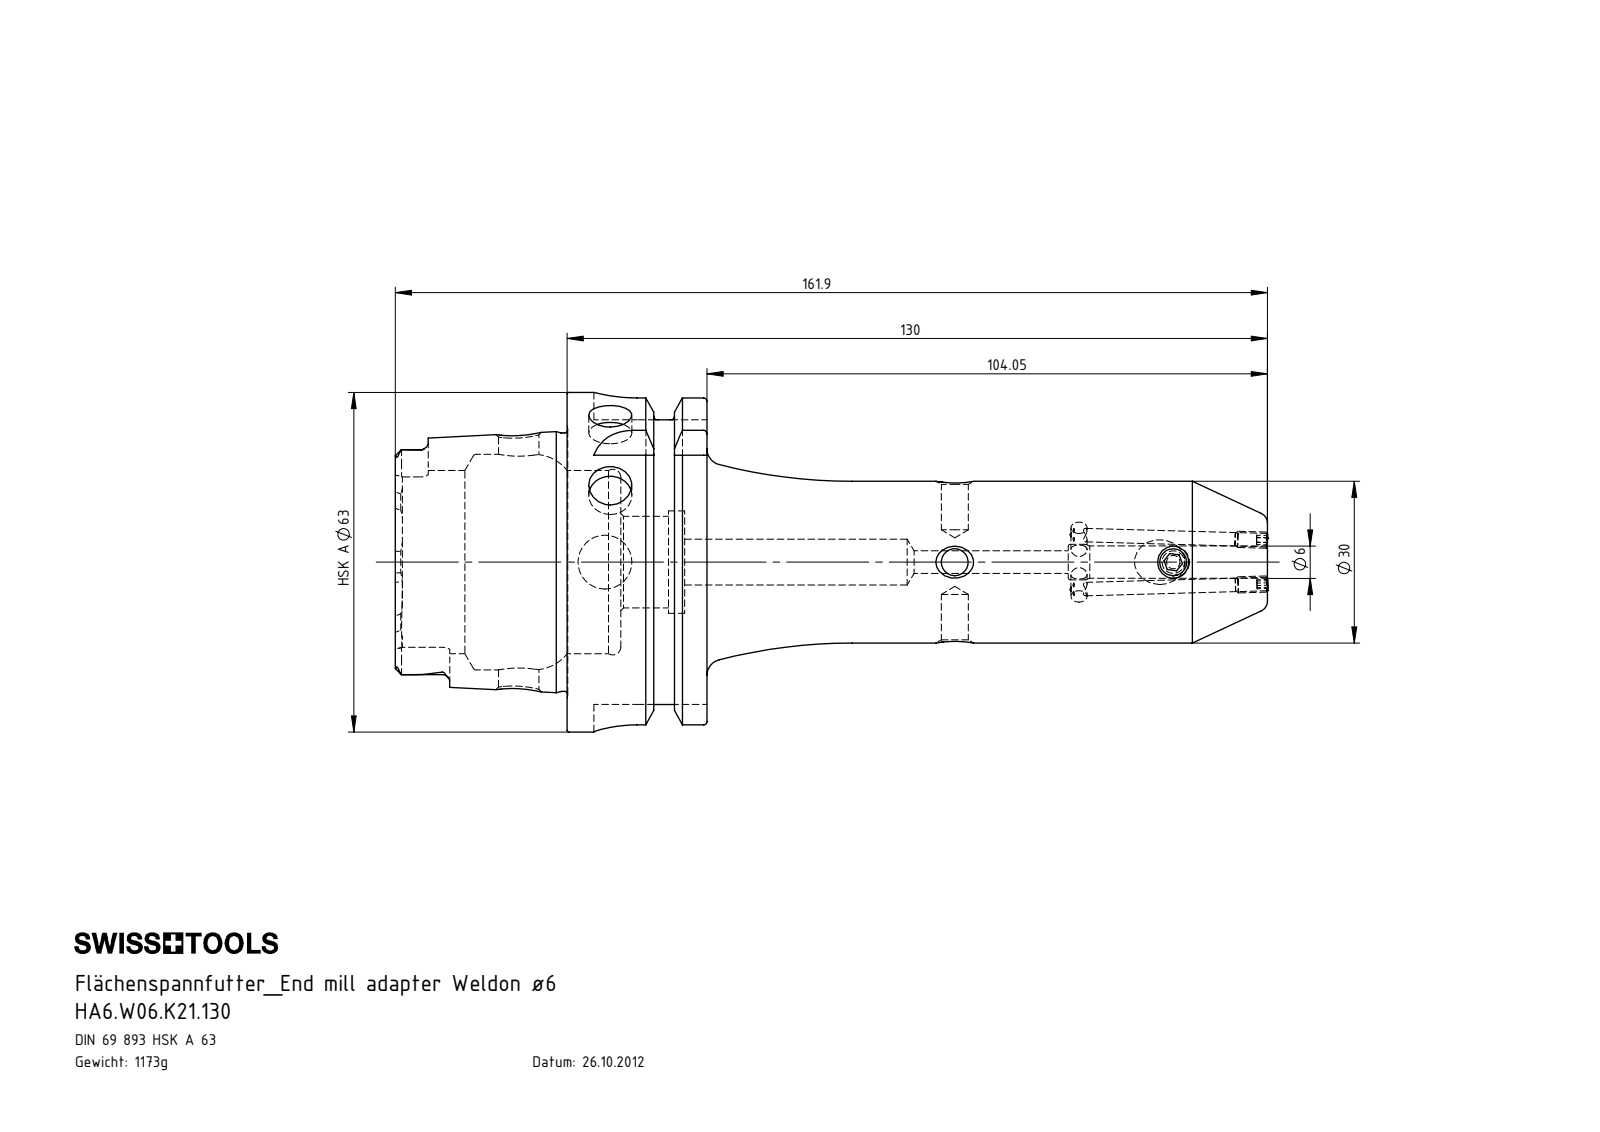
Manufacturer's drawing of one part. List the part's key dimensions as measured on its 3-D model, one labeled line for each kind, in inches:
Part name (STEP PRODUCT): HA6-W06.K21.130; ERU-CJ2.001.006; W06-ER1.001.010; HA6-W06.K21.130_A_Fertigbearbeitung
STEP written by: SolidWorks 2012 (CONFIG_CONTROL_DESIGN)
Units: inches
Bodies: 4 solids, 292 faces (77 planar, 83 cylindrical, 132 other)
Overall size (bounding box): 6.377 × 2.48 × 2.48
Volume: 9.118 in³ · Surface area: 54.63 in²
Round holes (diameter × count): ⌀0.197 ×3, ⌀0.098 ×2, ⌀0.315 ×2, ⌀0.118 ×1, ⌀0.165 ×1, ⌀0.236 ×1, ⌀0.26 ×1, ⌀0.295 ×1, ⌀0.335 ×1, ⌀0.394 ×1, ⌀0.669 ×1, ⌀0.748 ×1
Round bosses / shafts (diameter × count): ⌀0.118 ×2, ⌀2.48 ×1, ⌀2.163 ×1, ⌀1.887 ×1, ⌀1.181 ×1, ⌀0.236 ×1
Partial cylindrical surfaces — rounded edges, fillets, slot ends (radius × count): R0.055 ×6, R0.113 ×4, R0.315 ×4
Main face-to-face distances: 1.022, 0.63, 0.392, 1.256, 1.648, 2.278, 2.079, 0.858, 0.467, 2.114
Hole centre spacings: 1.596, 2.557, 3.187, 4.154
